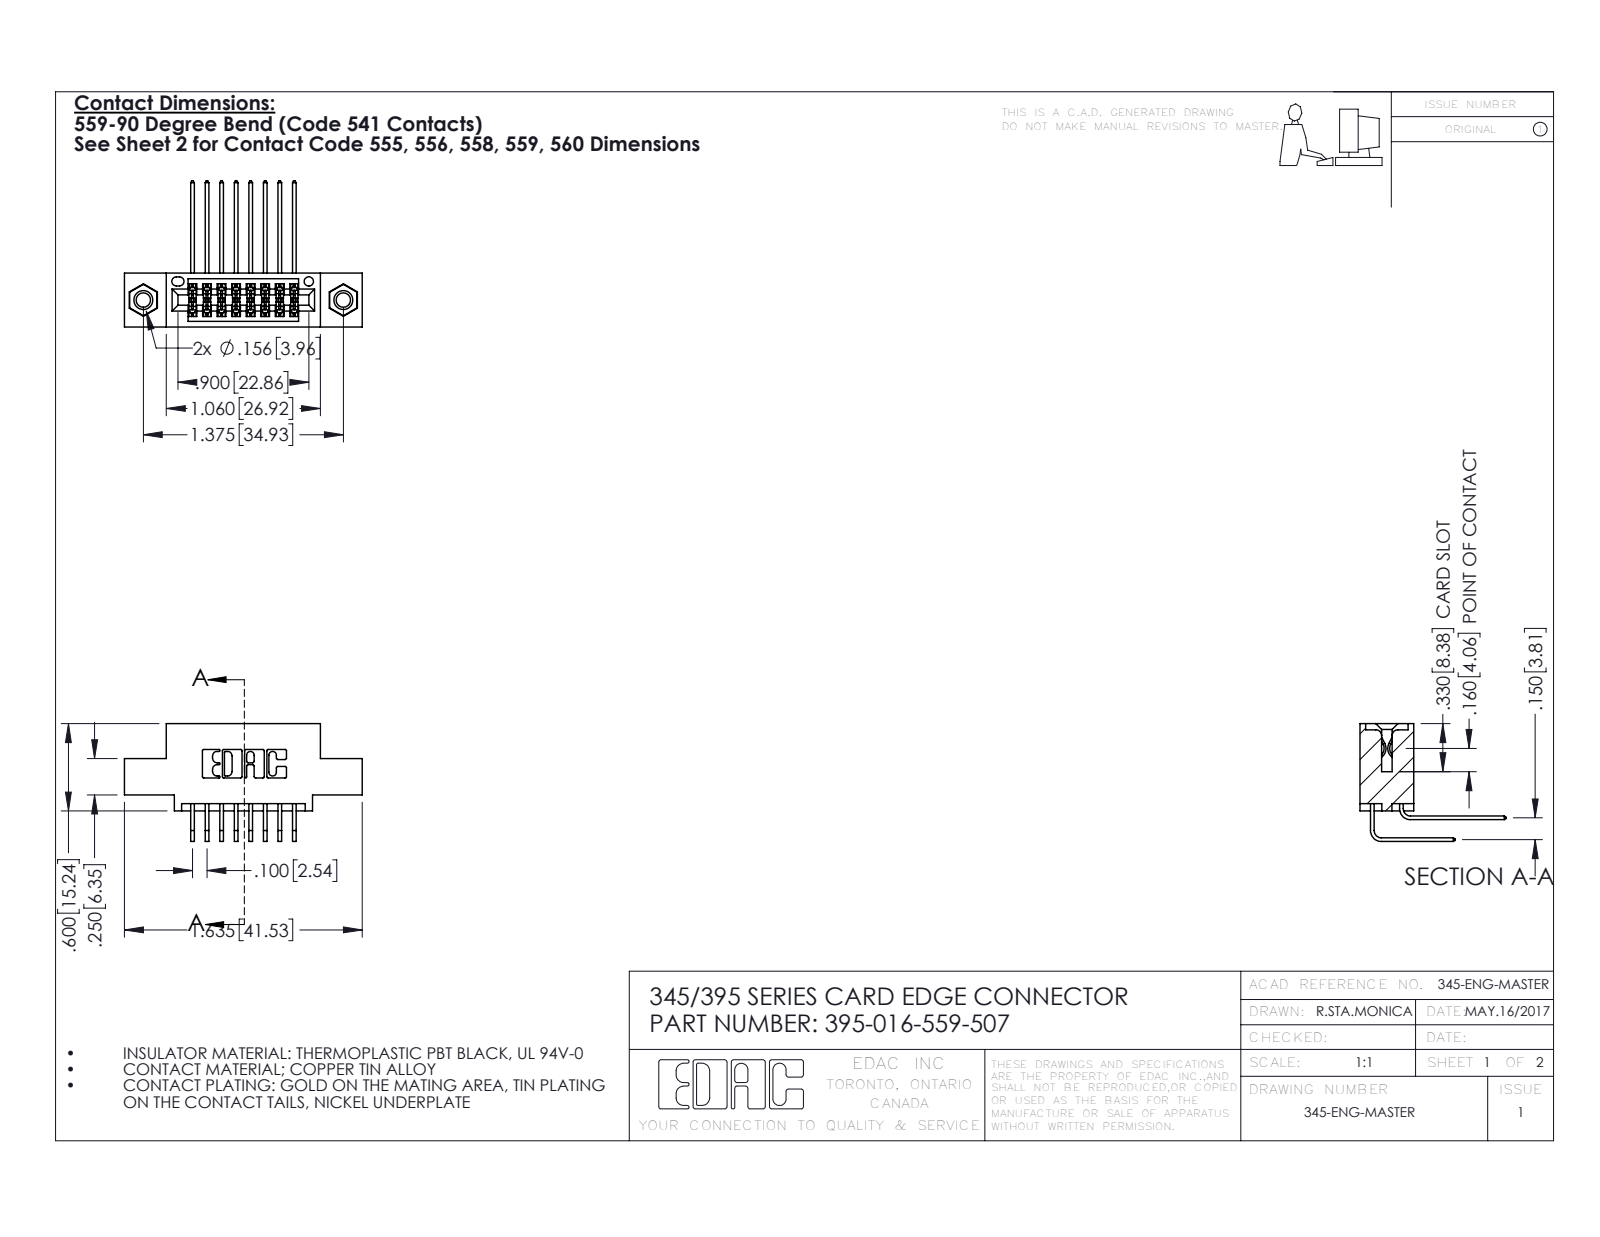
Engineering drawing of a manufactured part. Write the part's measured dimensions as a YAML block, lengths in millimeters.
part_name: "345-292-001_559 Tail - 2; 395-016-559-507; 345-292-001_558 559 Tail - 1; 345-250-001_345-250-005-103 (+1 more)"
step_written_by: "SolidWorks 2016 (CONFIG_CONTROL_DESIGN)"
units: millimeters
bodies: {solids: 19, faces: 1022, planar: 676, cylindrical: 330, other: 16}
overall_size: [41.5, 25.5, 20.5]
volume: 3720
surface_area: 5401
round_holes:
  - {diameter: 2.5, count: 2}
  - {diameter: 3.2, count: 2}
  - {diameter: 4, count: 2}
  - {diameter: 1.6, count: 1}
round_bosses_or_shafts:
  - {diameter: 3.9, count: 2}
partial_cylinders:
  - {radius: 0.2, count: 25}
  - {radius: 0.3, count: 22}
  - {radius: 0.2, count: 6}
  - {radius: 0.8, count: 6}
  - {radius: 0.7, count: 3}
  - {radius: 0.4, count: 2}
  - {radius: 0.5, count: 2}
  - {radius: 0.6, count: 2}
face_to_face_distances: [5.1, 1.8, 7.6, 9.4, 2.5, 7.6, 2.5, 6.9, 0.6, 4.1]
hole_center_spacings: [6.9, 29.1, 34.9]
